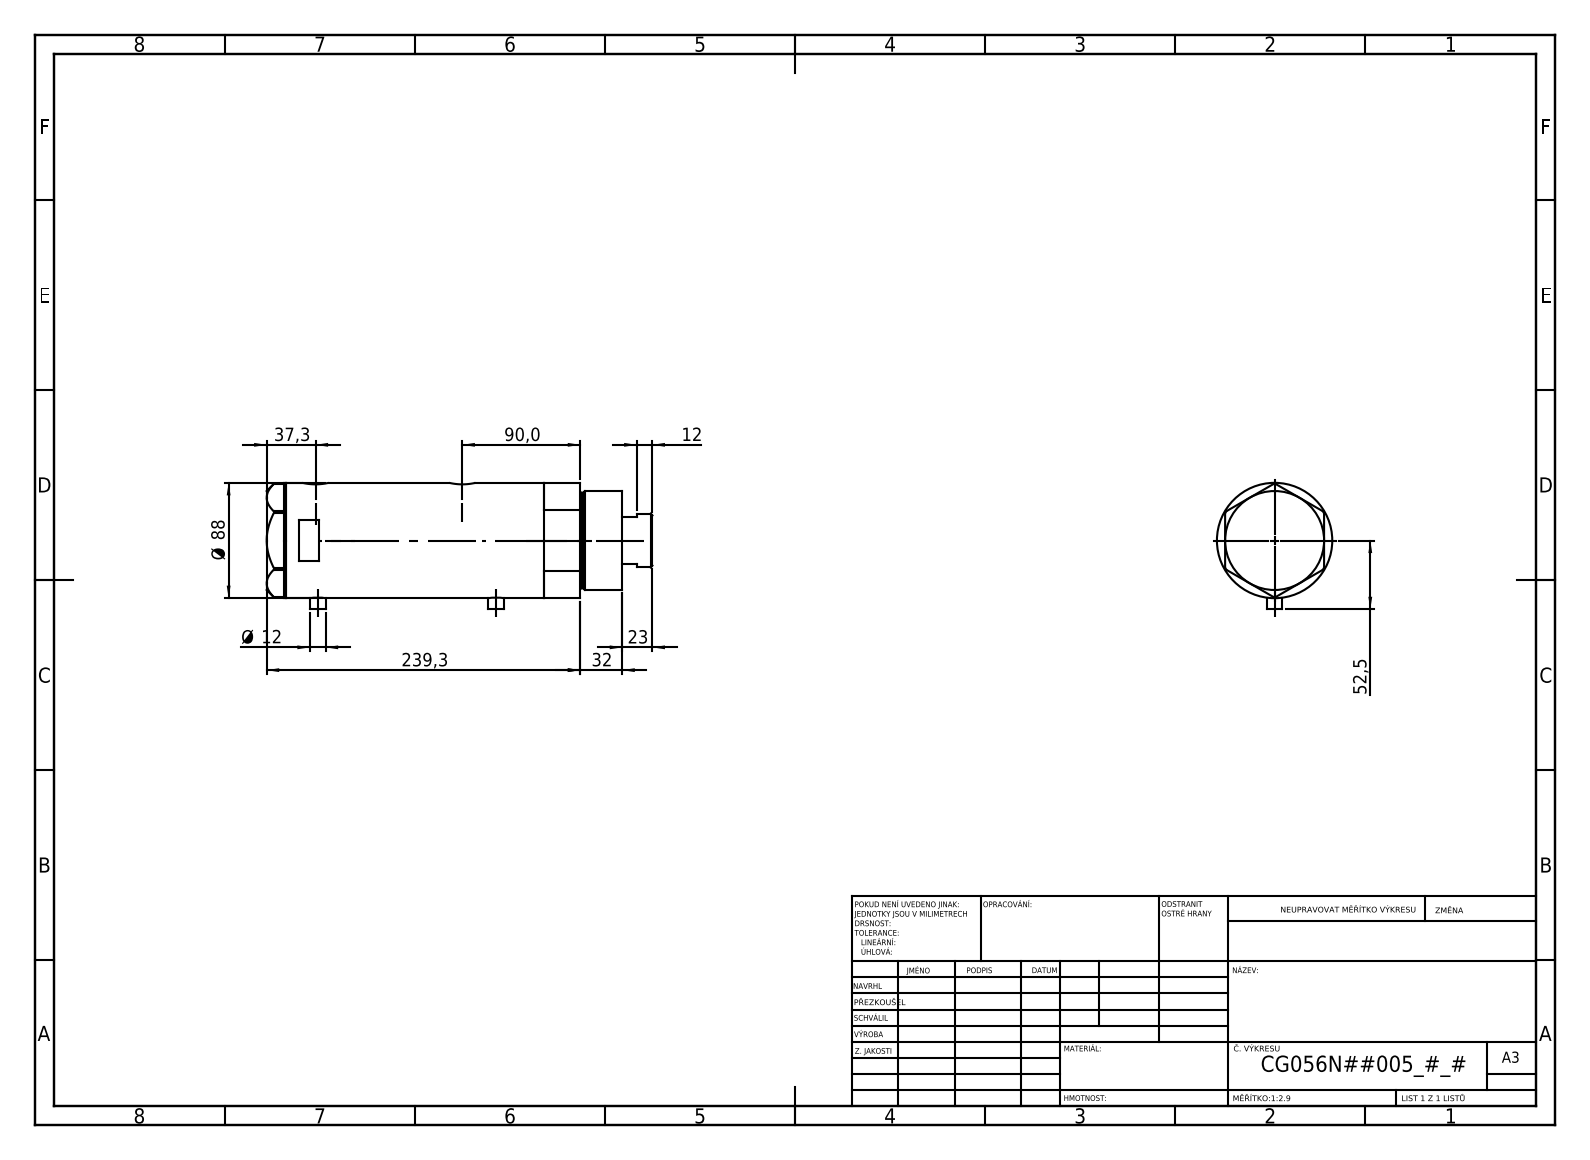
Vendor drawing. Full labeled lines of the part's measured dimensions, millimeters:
Part name (STEP PRODUCT): V270CG_MIDDLE; V270CG_FRONT; V270CG_VC; V270CG_BACK
STEP written by: SolidWorks 2019 (CONFIG_CONTROL_DESIGN)
Units: millimetres
Bodies: 4 solids, 121 faces (52 planar, 49 cylindrical, 20 other)
Overall size (bounding box): 294.3 × 96.5 × 88
Volume: 1 583 000 mm³ · Surface area: 223 413 mm²
Round holes (diameter × count): ⌀12.5 ×2, ⌀13.16 ×2, ⌀20 ×2, ⌀14.5 ×1, ⌀42 ×1, ⌀43.5 ×1, ⌀56 ×1, ⌀60 ×1, ⌀80 ×1
Round bosses / shafts (diameter × count): ⌀12 ×2, ⌀88 ×1, ⌀75 ×1, ⌀73 ×1, ⌀41 ×1
Main face-to-face distances: 134.4, 26, 108.4, 15, 41, 149.4, 256.3, 271.3, 230.3, 121.9
Hole centre spacings: 1.7, 25.8, 110.3, 112, 136.1, 137.8
